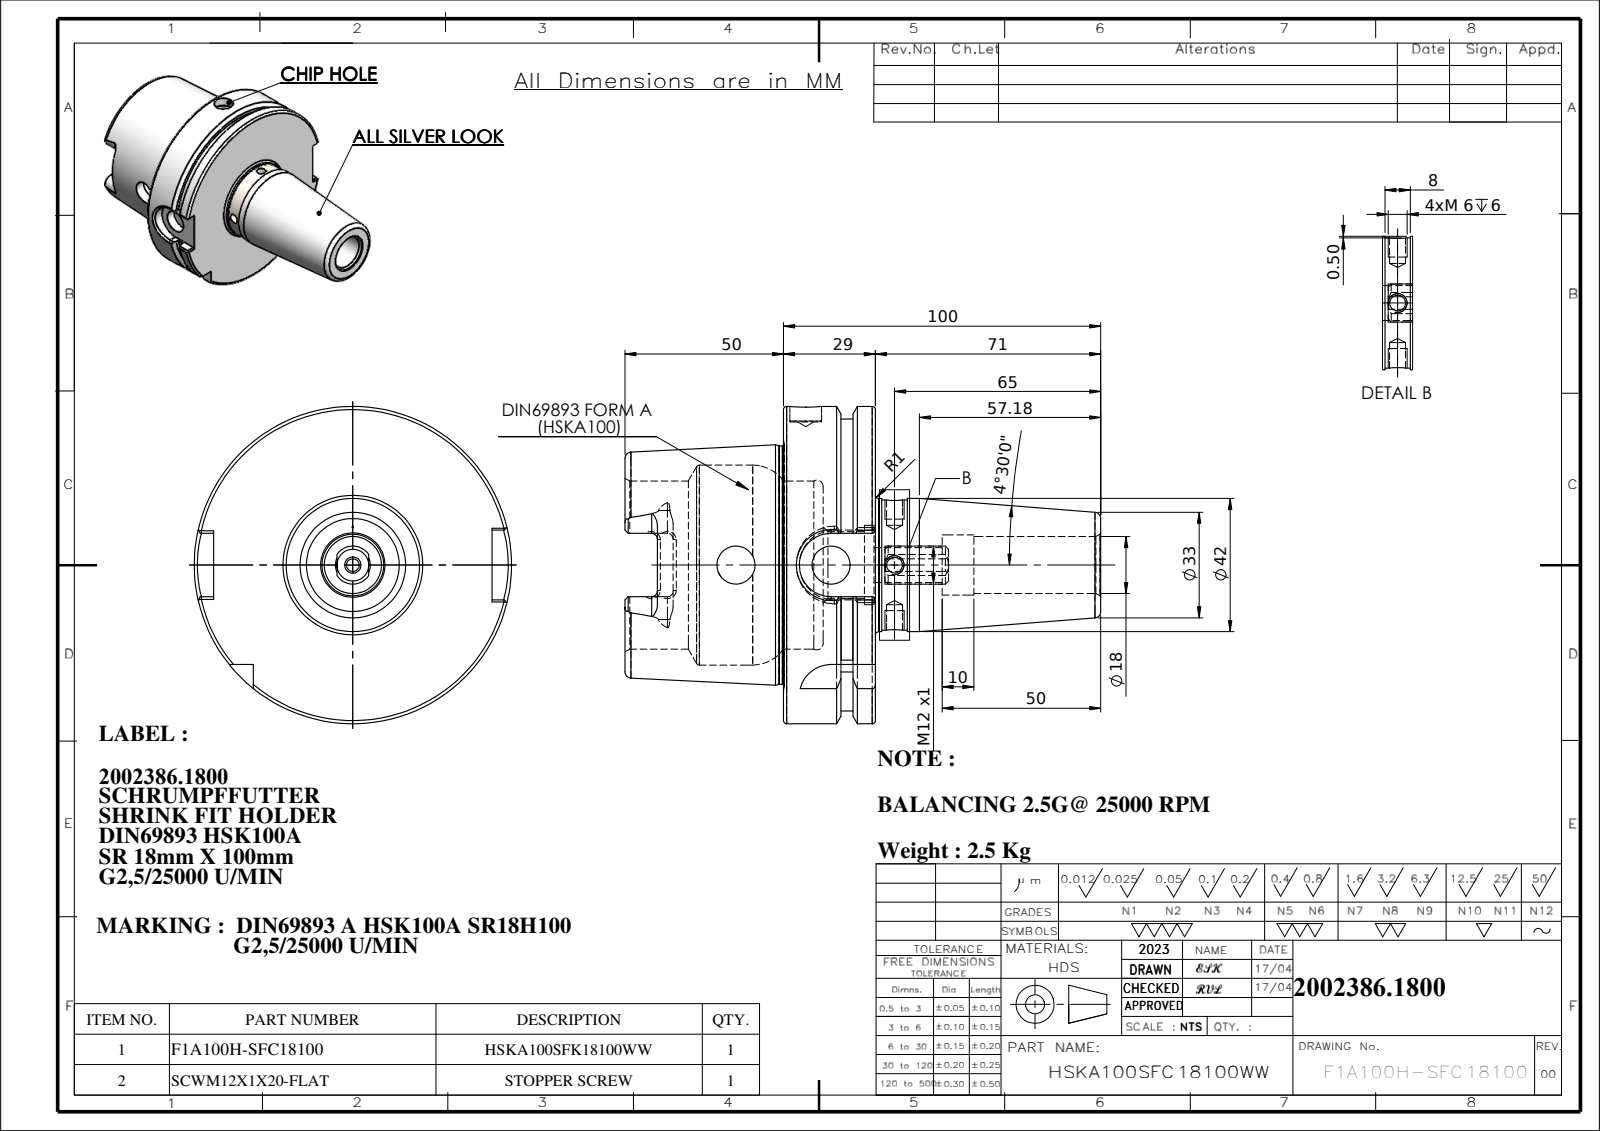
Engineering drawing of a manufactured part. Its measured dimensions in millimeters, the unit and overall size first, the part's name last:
Units: millimetres
Overall size (bounding box): 150 × 100 × 100
Round holes (diameter × count): ⌀5 ×2, ⌀12 ×2, ⌀4 ×1, ⌀10 ×1, ⌀11 ×1, ⌀17.99 ×1, ⌀18.99 ×1, ⌀21 ×1, ⌀25 ×1, ⌀53 ×1, ⌀63 ×1
Round bosses / shafts (diameter × count): ⌀100 ×1, ⌀92 ×1, ⌀75.16 ×1, ⌀42 ×1, ⌀41 ×1
Partial cylindrical surfaces — rounded edges, fillets, slot ends (radius × count): R1.8 ×6, R4.88 ×4, R10 ×2, R6 ×1, R11 ×1
Main face-to-face distances: 28.95, 12.5, 16.45, 50, 62.5, 78.95, 100, 71.88, 21.88, 9.38
Hole centre spacings: 20, 28, 30, 50
Volume: 321 832 mm³ · Surface area: 62 997 mm²
Bodies: 2 solids, 216 faces (59 planar, 69 cylindrical, 88 other)
Part name (STEP PRODUCT): HSKA100SFC18100WW; SCWM12X1X20-FLAT; 91100A-SR18100
STEP written by: SolidWorks 2018 (CONFIG_CONTROL_DESIGN)
